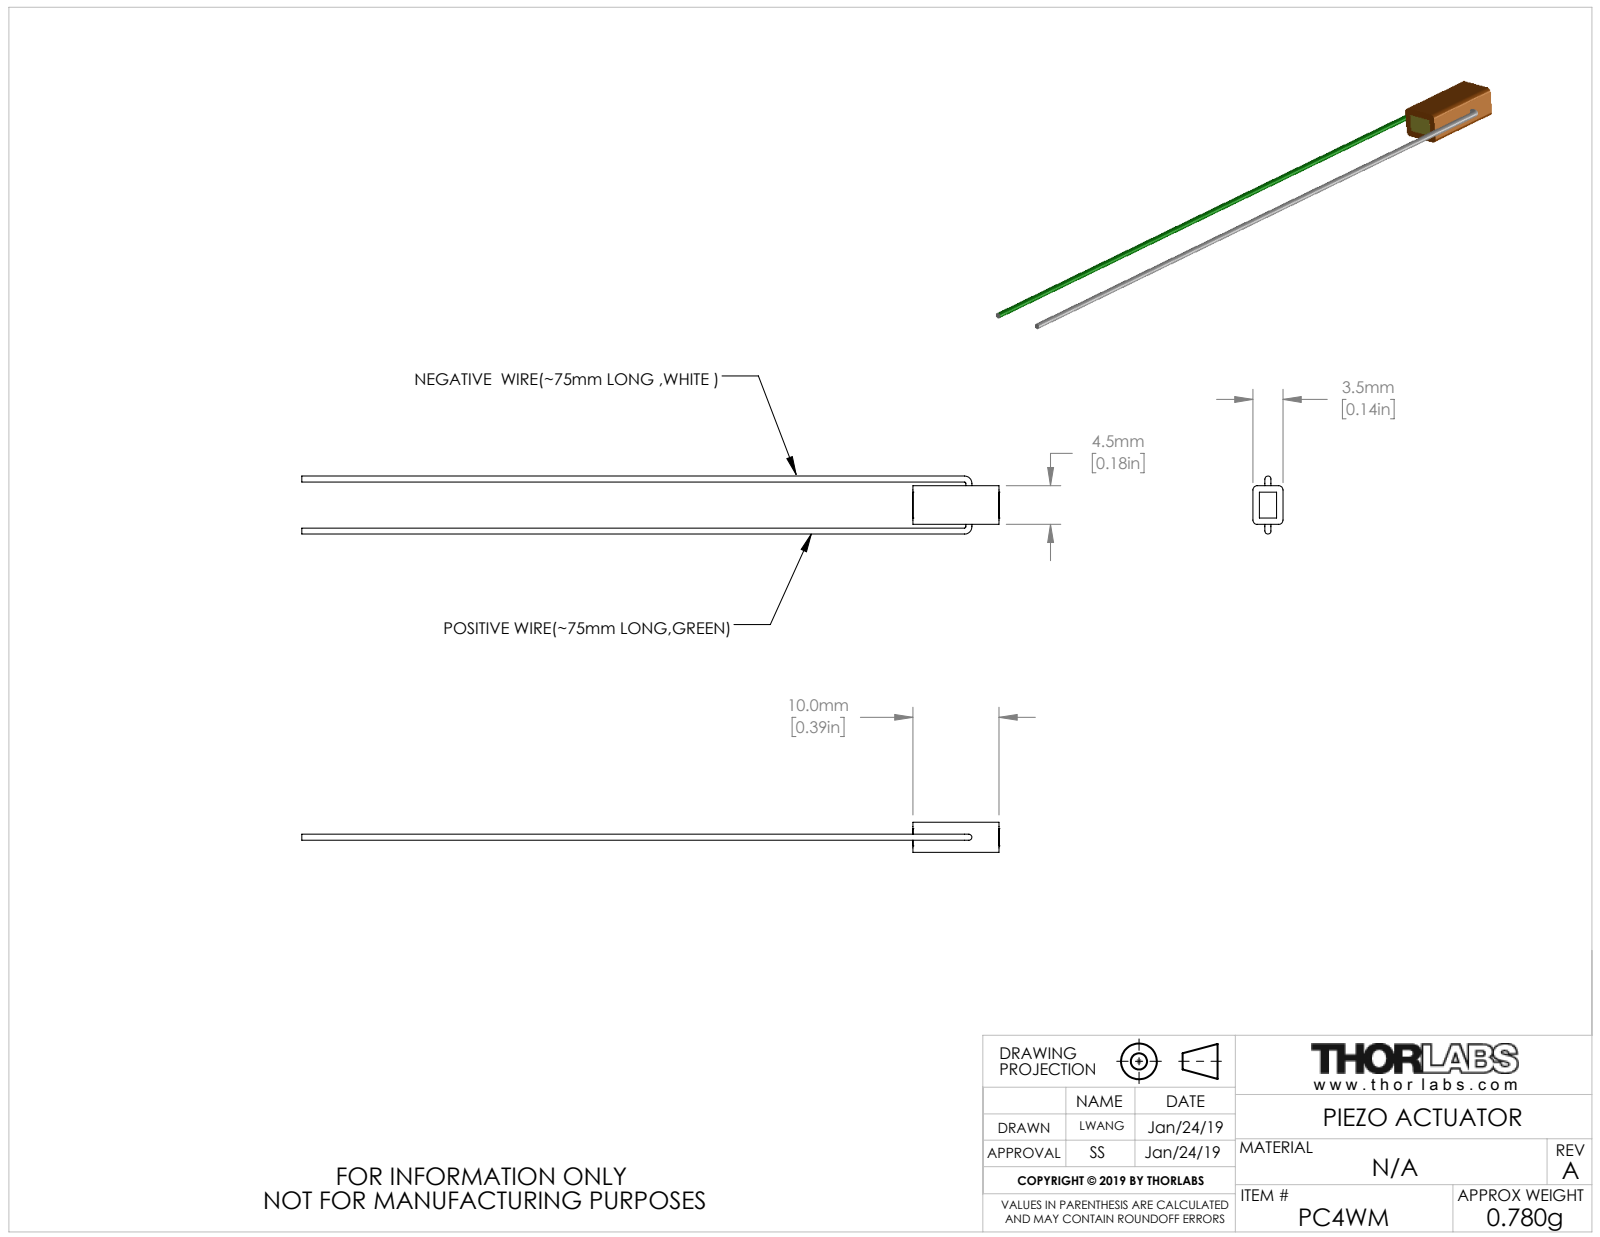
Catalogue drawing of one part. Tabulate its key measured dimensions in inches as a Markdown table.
| quantity | value |
| --- | --- |
| part name | CTN013638 |
| STEP written by | SolidWorks 2018 (AUTOMOTIVE_DESIGN) |
| units | inches |
| bodies | 1 solid, 38 faces (18 planar, 16 cylindrical, 4 other) |
| overall size | 3.195 × 0.266 × 0.138 |
| volume | 0.013 in³ |
| surface area | 0.817 in² |
| round bosses / shafts (diameter × count) | 0.028 × 3 |
| partial cylindrical surfaces (radius × count) | 0.02 × 4 |
| main face-to-face distances | 0.138, 0.177, 0.394, 0.394, 0.394, 2.801, 2.801, 3.195, 3.195, 0.03 |
